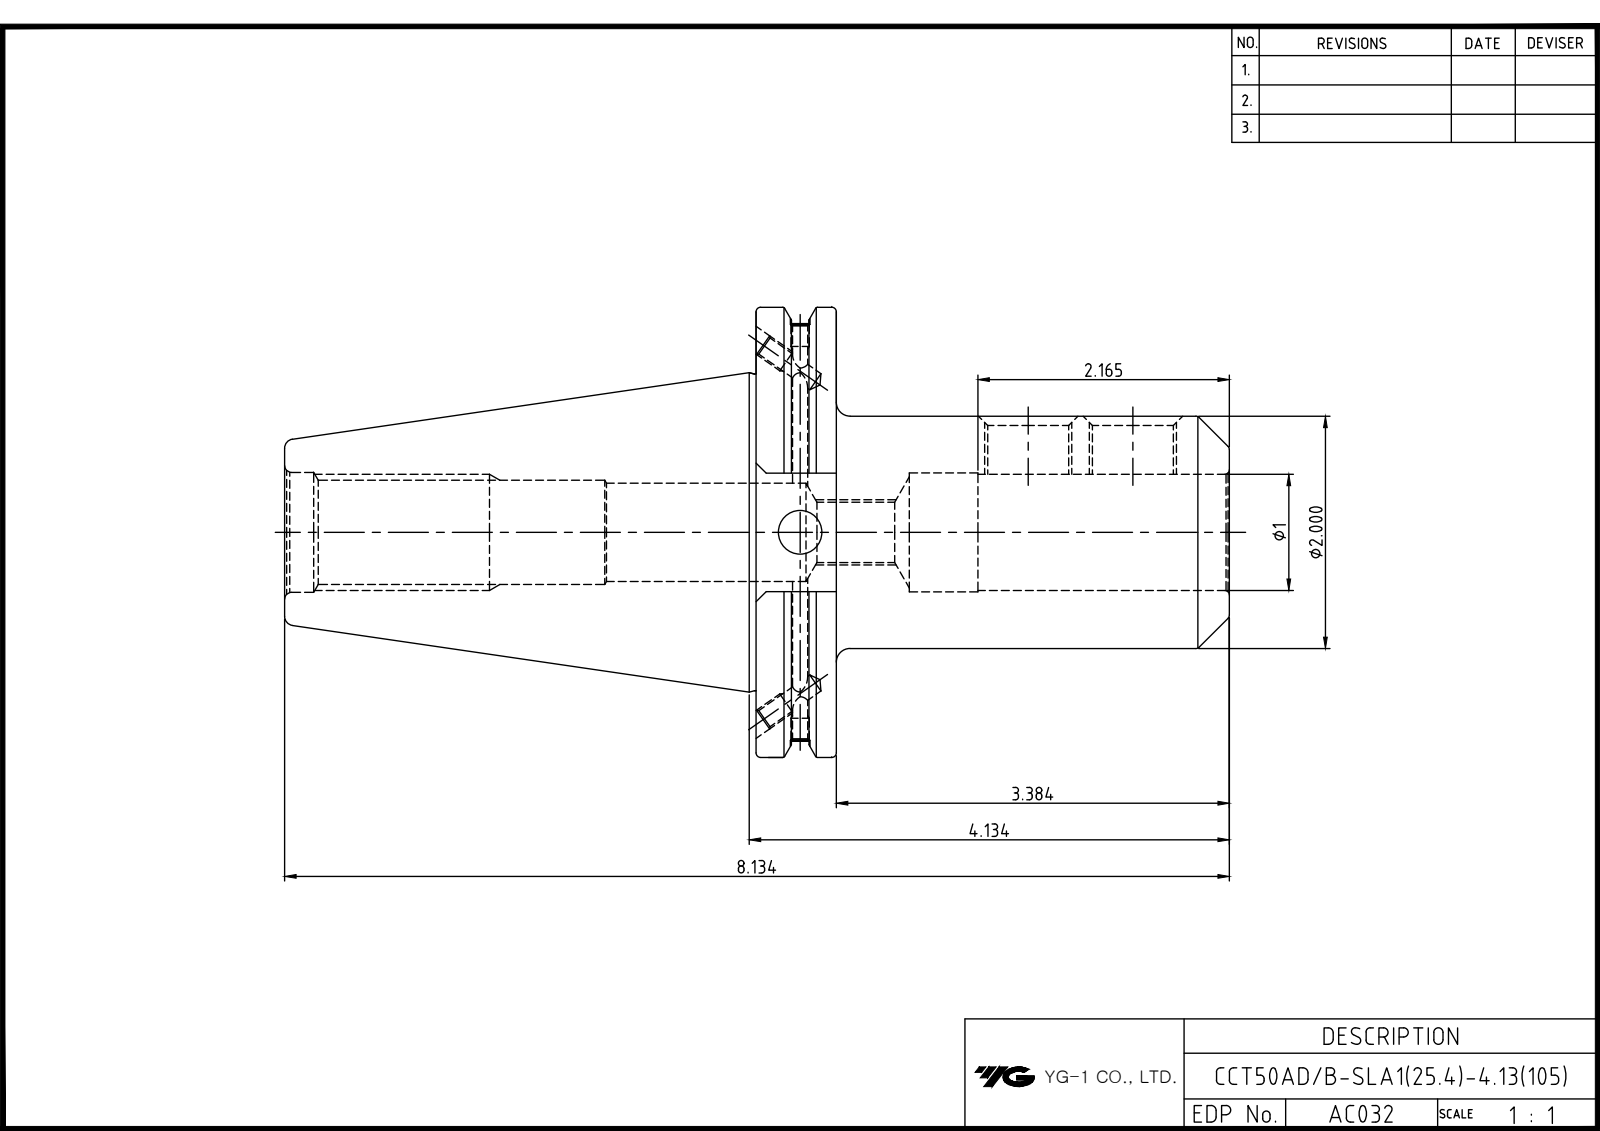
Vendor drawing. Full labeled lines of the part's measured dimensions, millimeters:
Part name (STEP PRODUCT): LO-CCT50ADB-SLA25.4-105
STEP written by: Autodesk Inventor 2025 (AUTOMOTIVE_DESIGN)
Units: millimetres
Bodies: 1 solid, 93 faces (40 planar, 28 cylindrical, 25 other)
Overall size (bounding box): 206.6 × 98.42 × 94.69
Volume: 450 719 mm³ · Surface area: 64 820 mm²
Round holes (diameter × count): ⌀3.24 ×2, ⌀4.13 ×2, ⌀4.2 ×2, ⌀5 ×2, ⌀17.32 ×2, ⌀9.53 ×1, ⌀12.57 ×1, ⌀21.97 ×1, ⌀25.4 ×1, ⌀26.2 ×1, ⌀26.6 ×1
Round bosses / shafts (diameter × count): ⌀98.42 ×1, ⌀91.29 ×1, ⌀69.25 ×1, ⌀50.8 ×1
Main face-to-face distances: 17.55, 103.1, 103.5, 120.65, 206.6, 85.95, 136.6, 33.5, 15.95, 70
Hole centre spacings: 22.9
